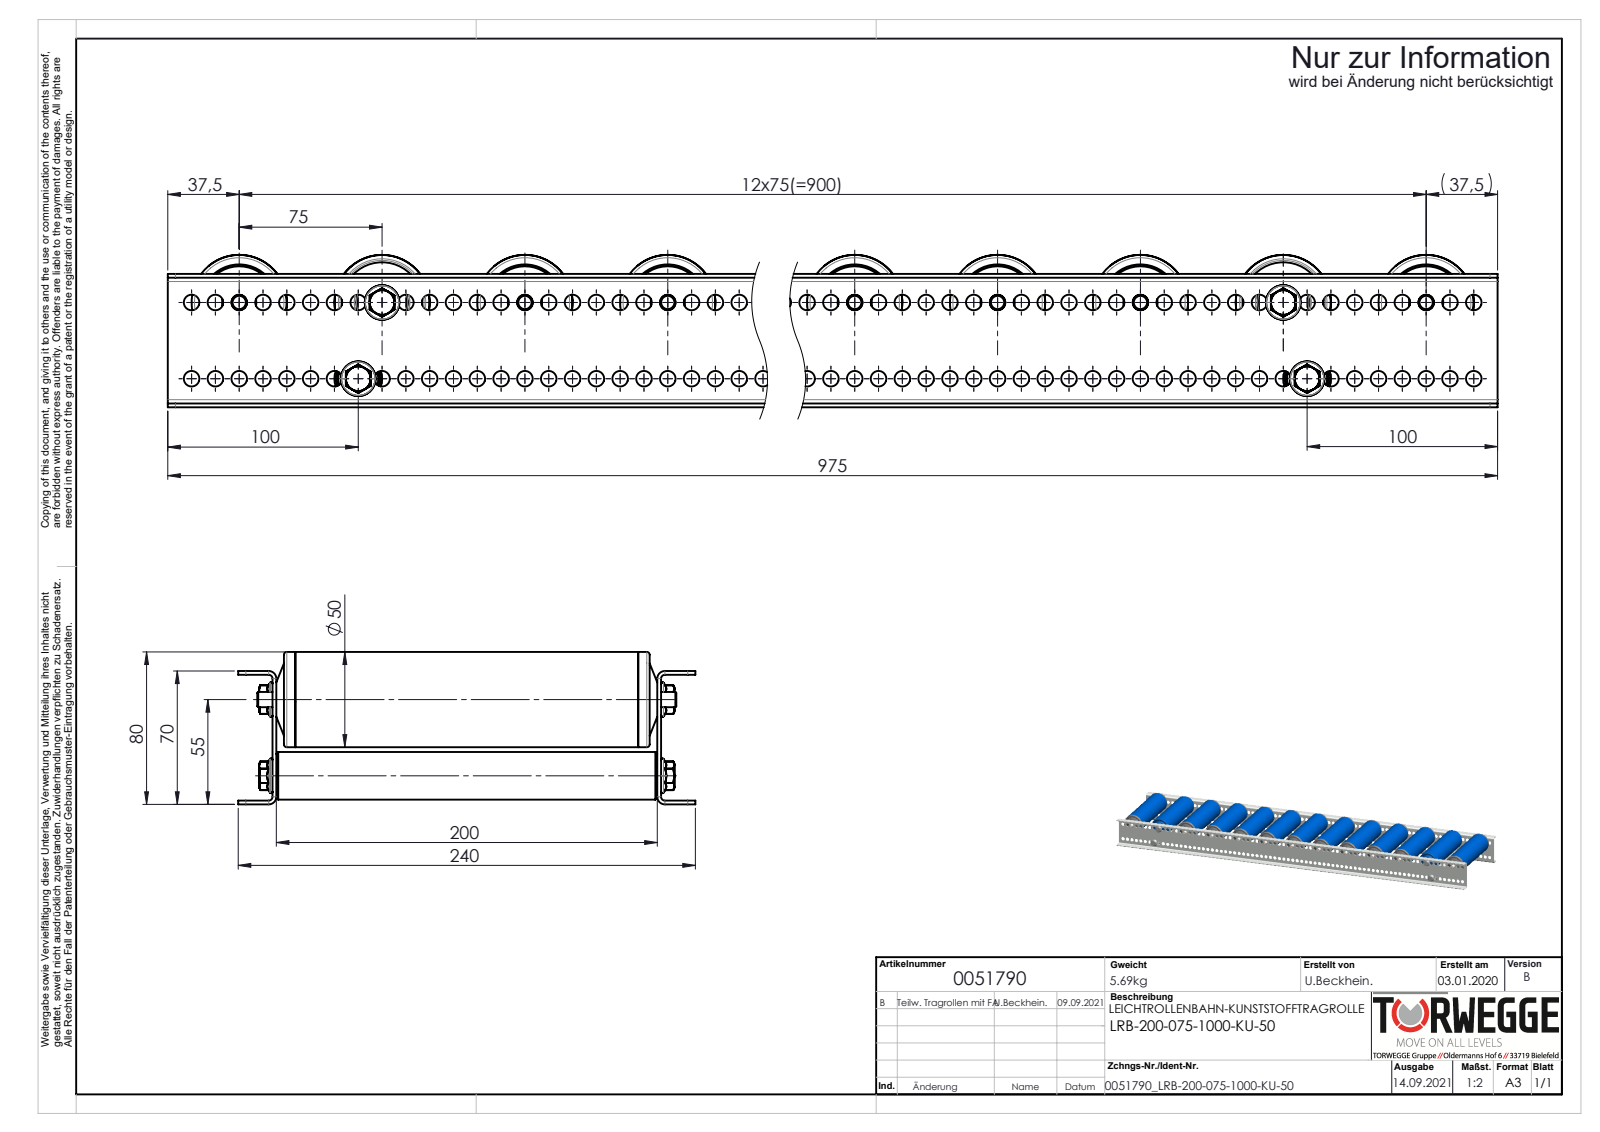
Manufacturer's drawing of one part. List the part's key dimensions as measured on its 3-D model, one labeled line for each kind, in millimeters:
Part name (STEP PRODUCT): KUT100-50x2,8-KB-A12-IGM8-EL=KFG_S100912_KUT100-50x2,8-KB-A12-IGM8-EL=200; 0017015_Tragrollenrohr-Ø50x2,8KU_KFG_0017015_L=185; Profil_LRB-20x70x20x2_KFG_S100213_U-PROFIL-20-70-20-2-LRB-L=975; 0024178_Passscheibe_DIN988_12x18x1 (+8 more)
STEP written by: SolidWorks 2020 (AUTOMOTIVE_DESIGN)
Units: millimetres
Bodies: 241 solids, 4450 faces (1148 planar, 1900 cylindrical, 1402 other)
Overall size (bounding box): 975 × 240 × 80
Volume: 2 291 000 mm³ · Surface area: 1 787 000 mm²
Round holes (diameter × count): ⌀8.2 ×154, ⌀7.6 ×11, ⌀8 ×11, ⌀25 ×11, ⌀30 ×11, ⌀35 ×11, ⌀39.4 ×11, ⌀40 ×11, ⌀6.8 ×4, ⌀12 ×2, ⌀12.1 ×2, ⌀16 ×2
Round bosses / shafts (diameter × count): ⌀50 ×13, ⌀44.4 ×11, ⌀38 ×11, ⌀36 ×11, ⌀33 ×11, ⌀22 ×11, ⌀21 ×11, ⌀25 ×4
Partial cylindrical surfaces — rounded edges, fillets, slot ends (radius × count): R0.6 ×22, R0.75 ×22, R2.45 ×22, R4.87 ×11, R7 ×11, R4 ×8, R2 ×4
Main face-to-face distances: 2, 202, 68, 200, 204, 66, 70, 192, 6, 12
Hole centre spacings: 12.5, 25, 37.5, 50, 62.5, 75, 87.5, 100
